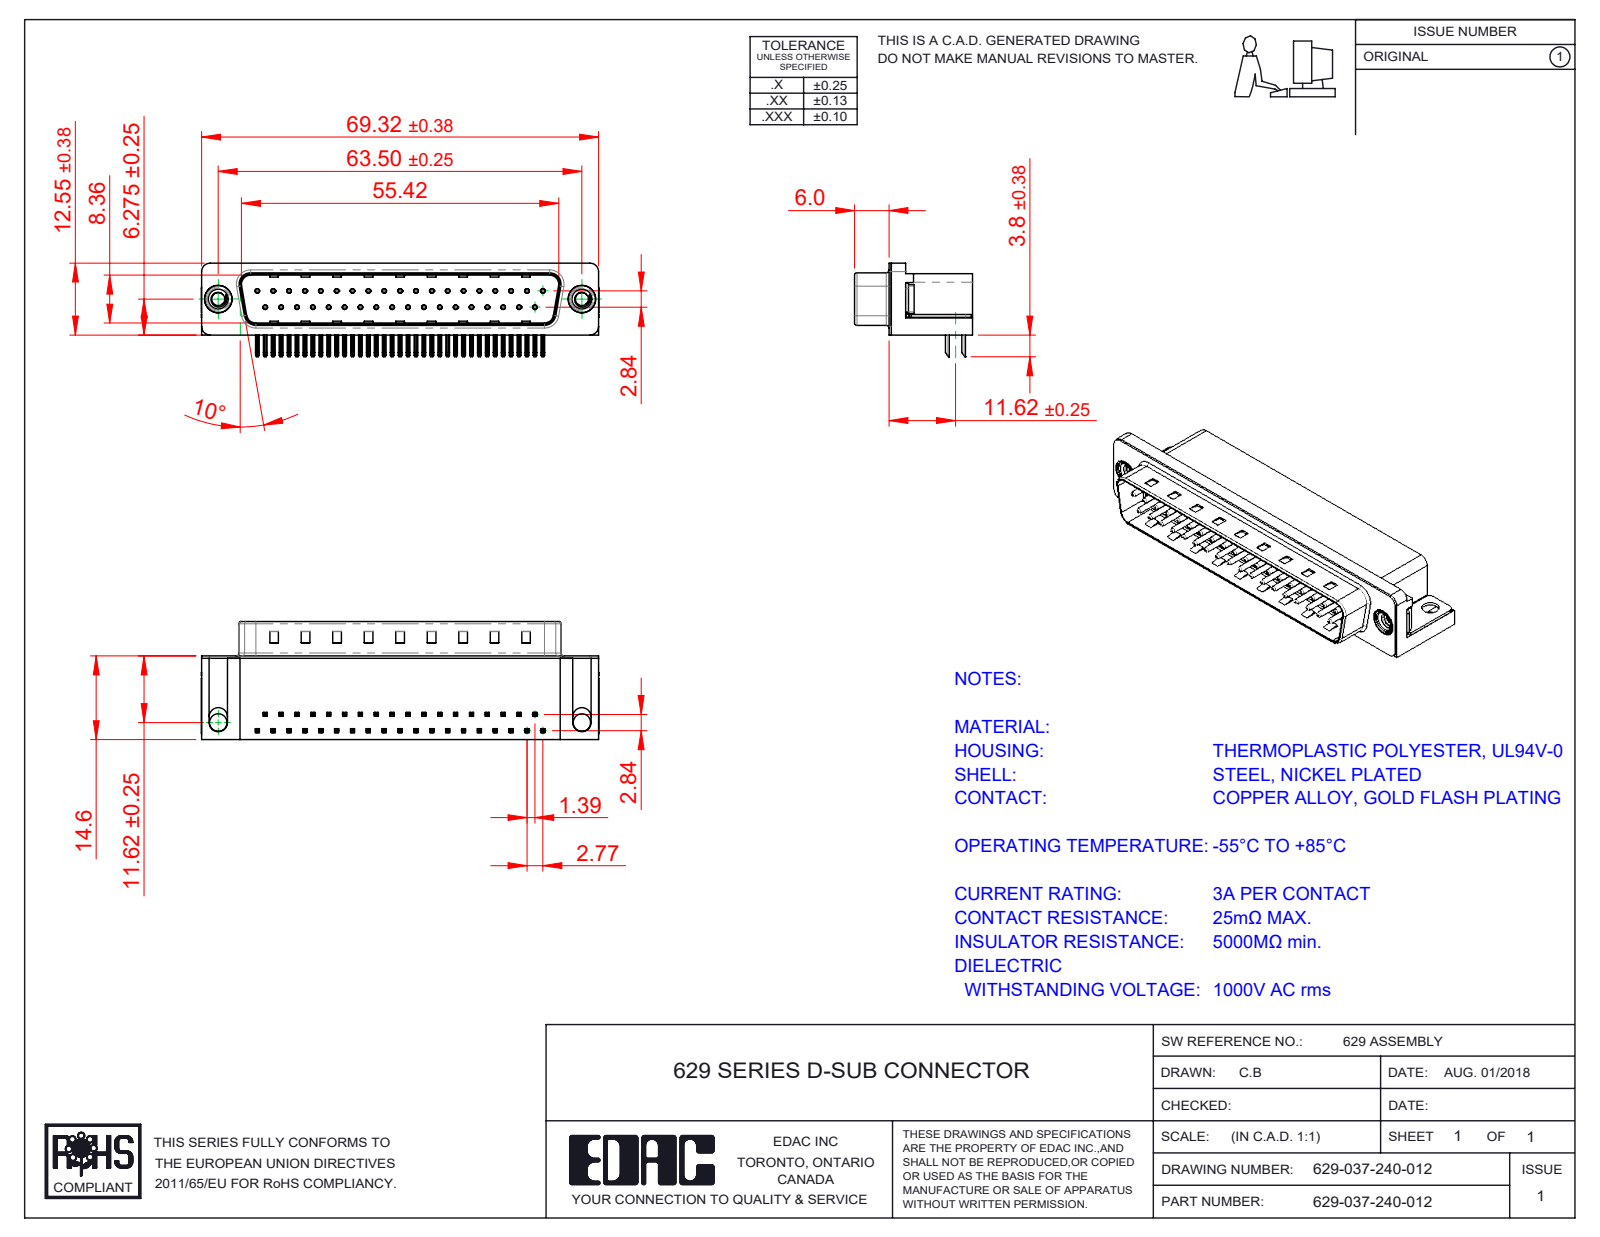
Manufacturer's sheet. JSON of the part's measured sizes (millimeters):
{"part_name": "629 Contact Bottom; 629 Contact Top; 629-037-240-012; 629 Thru Hole Board Mount (+3 more)", "step_written_by": "SolidWorks 2020 (CONFIG_CONTROL_DESIGN)", "units": "millimeters", "bodies": {"solids": 43, "faces": 3197, "planar": 2011, "cylindrical": 915, "other": 271}, "overall_size": [69.4, 20.6, 16.35], "volume_mm3": 9966, "surface_area_mm2": 10794, "round_holes": [[0.35, 37], [0.8, 37], [2.26, 2], [3.05, 2], [4, 2], [4.8, 2], [5, 2]], "round_bosses_or_shafts": [[0.75, 37], [4.9, 2], [4.75, 2], [3.9, 2]], "partial_cylinders_radius": [[0.25, 156], [0.12, 74], [1, 16], [0.5, 9], [1.6, 8], [1.5, 7], [0.9, 4], [2, 4]], "face_to_face_distances": [0.4, 10.35, 14.2, 8.76, 2.1, 1.7, 10.46, 10.86, 14.6, 10.11], "hole_center_spacings": [2.77, 3.16, 5.54, 8.31, 11.08, 13.85, 16.62, 19.39]}
